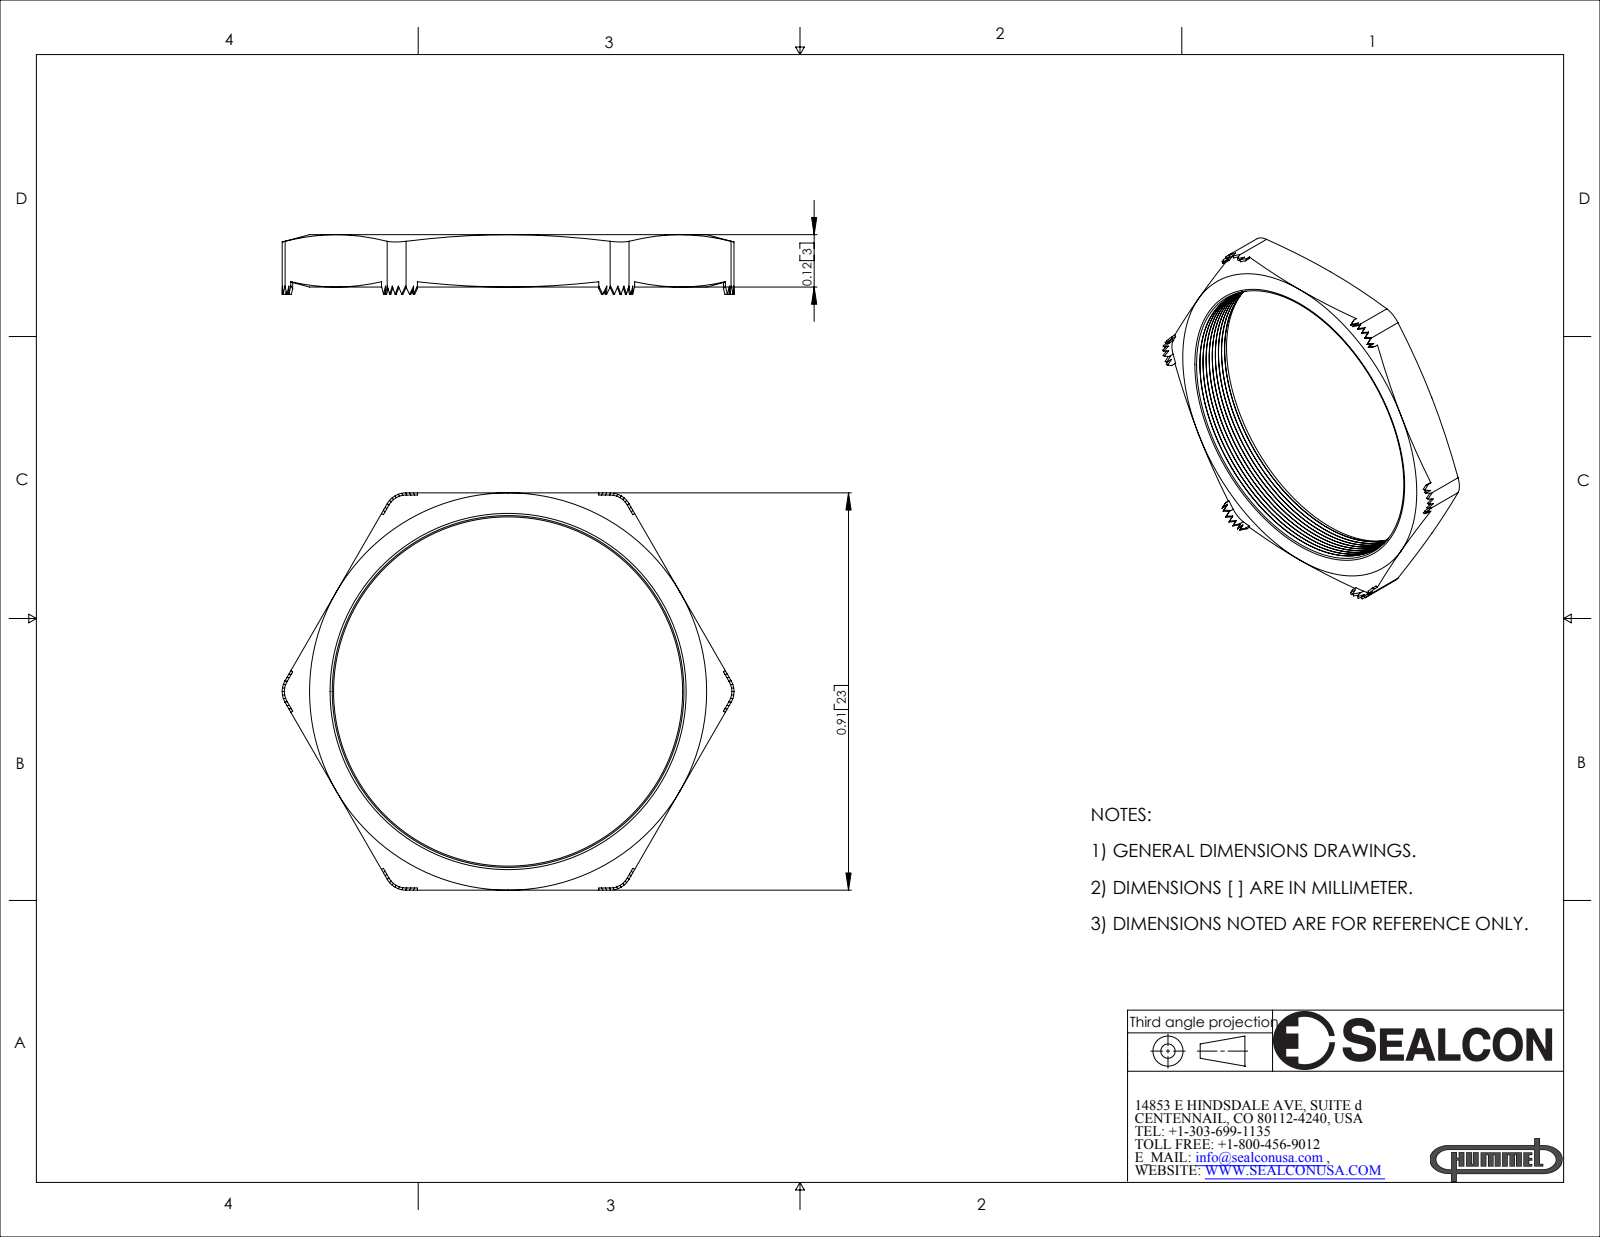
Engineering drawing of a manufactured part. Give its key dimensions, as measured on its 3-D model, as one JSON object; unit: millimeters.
{"part_name": "NP-13-BE", "step_written_by": "SolidWorks 2007 (CONFIG_CONTROL_DESIGN)", "units": "millimeters", "bodies": {"solids": 1, "faces": 206, "planar": 116, "cylindrical": 32, "other": 58}, "overall_size": [26.3, 23.1, 3.5], "volume_mm3": 380, "surface_area_mm2": 884, "round_holes": [[20.3, 1]], "partial_cylinders_radius": [[1.1, 6], [1.3, 6]], "face_to_face_distances": [23.1, 3, 23, 22.9, 0.4, 0.8, 0.4, 1.3, 0.6, 1.1]}
